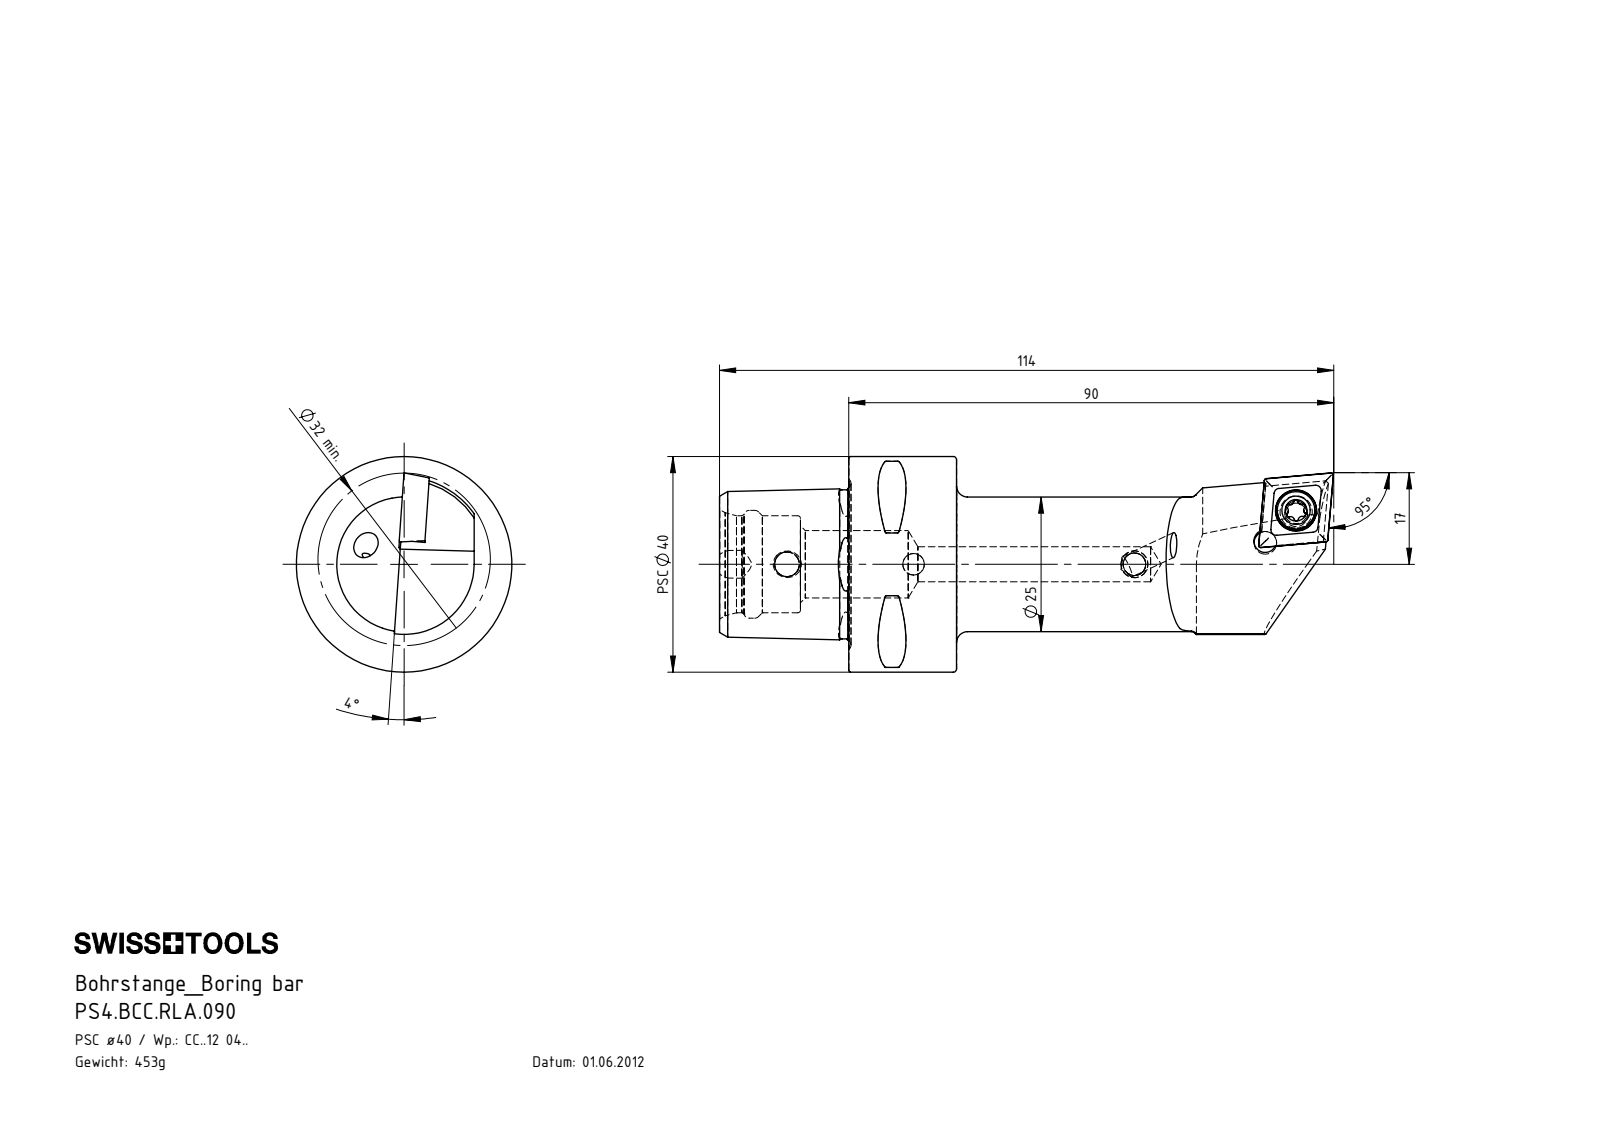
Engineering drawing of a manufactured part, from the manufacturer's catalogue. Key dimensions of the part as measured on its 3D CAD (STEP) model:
Part name (STEP PRODUCT): CCMT120404; PS4.BCC.RLA.090; PS4-BCC.RLA.090_A; WCC-ER2.001.010_A (+1 more)
STEP written by: SolidWorks 2017 (AUTOMOTIVE_DESIGN)
Units: millimetres
Bodies: 5 solids, 288 faces (49 planar, 74 cylindrical, 165 other)
Overall size (bounding box): 114 × 40 × 40
Volume: 57 707 mm³ · Surface area: 15 991 mm²
Round holes (diameter × count): ⌀4.2 ×4, ⌀4 ×2, ⌀4.6 ×1, ⌀5.5 ×1, ⌀6.5 ×1, ⌀7.6 ×1, ⌀12.5 ×1, ⌀18 ×1, ⌀20 ×1
Round bosses / shafts (diameter × count): ⌀5 ×2, ⌀40 ×1, ⌀25 ×1, ⌀7 ×1
Partial cylindrical surfaces — rounded edges, fillets, slot ends (radius × count): R0.3 ×8, R0.39 ×6, R0.69 ×3, R0.69 ×3, R3 ×2, R13 ×1, R15 ×1
Main face-to-face distances: 20, 4.45, 24, 44, 15.52, 35.3, 15, 9, 29, 4.76
Hole centre spacings: 8.09, 23.5, 41, 64.5
